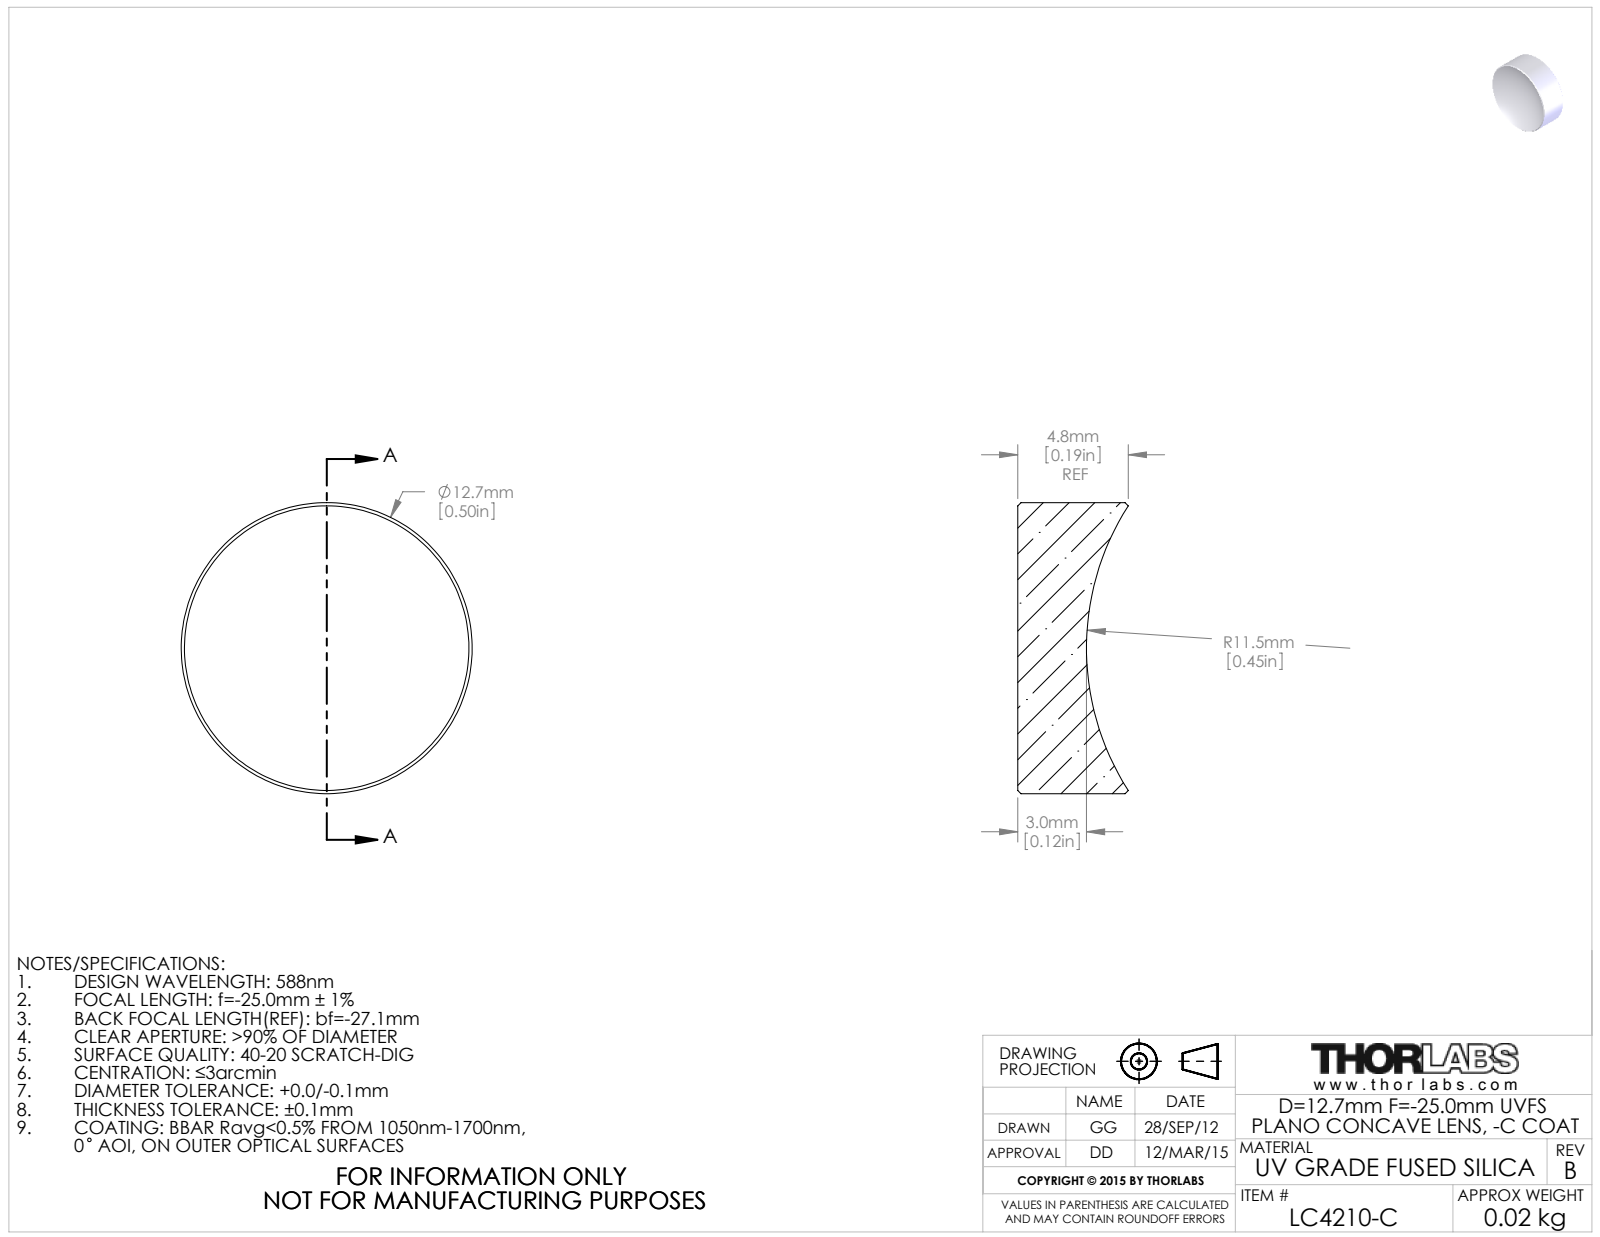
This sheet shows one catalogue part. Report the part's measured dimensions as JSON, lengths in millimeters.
{"part_name": "25019-E0W", "step_written_by": "SolidWorks 2011 (CONFIG_CONTROL_DESIGN)", "units": "millimeters", "bodies": {"solids": 1, "faces": 9, "planar": 1, "cylindrical": 2, "other": 6}, "overall_size": [12.7, 12.7, 4.82], "volume_mm3": 496, "surface_area_mm2": 449, "round_bosses_or_shafts": [[12.7, 1]]}
